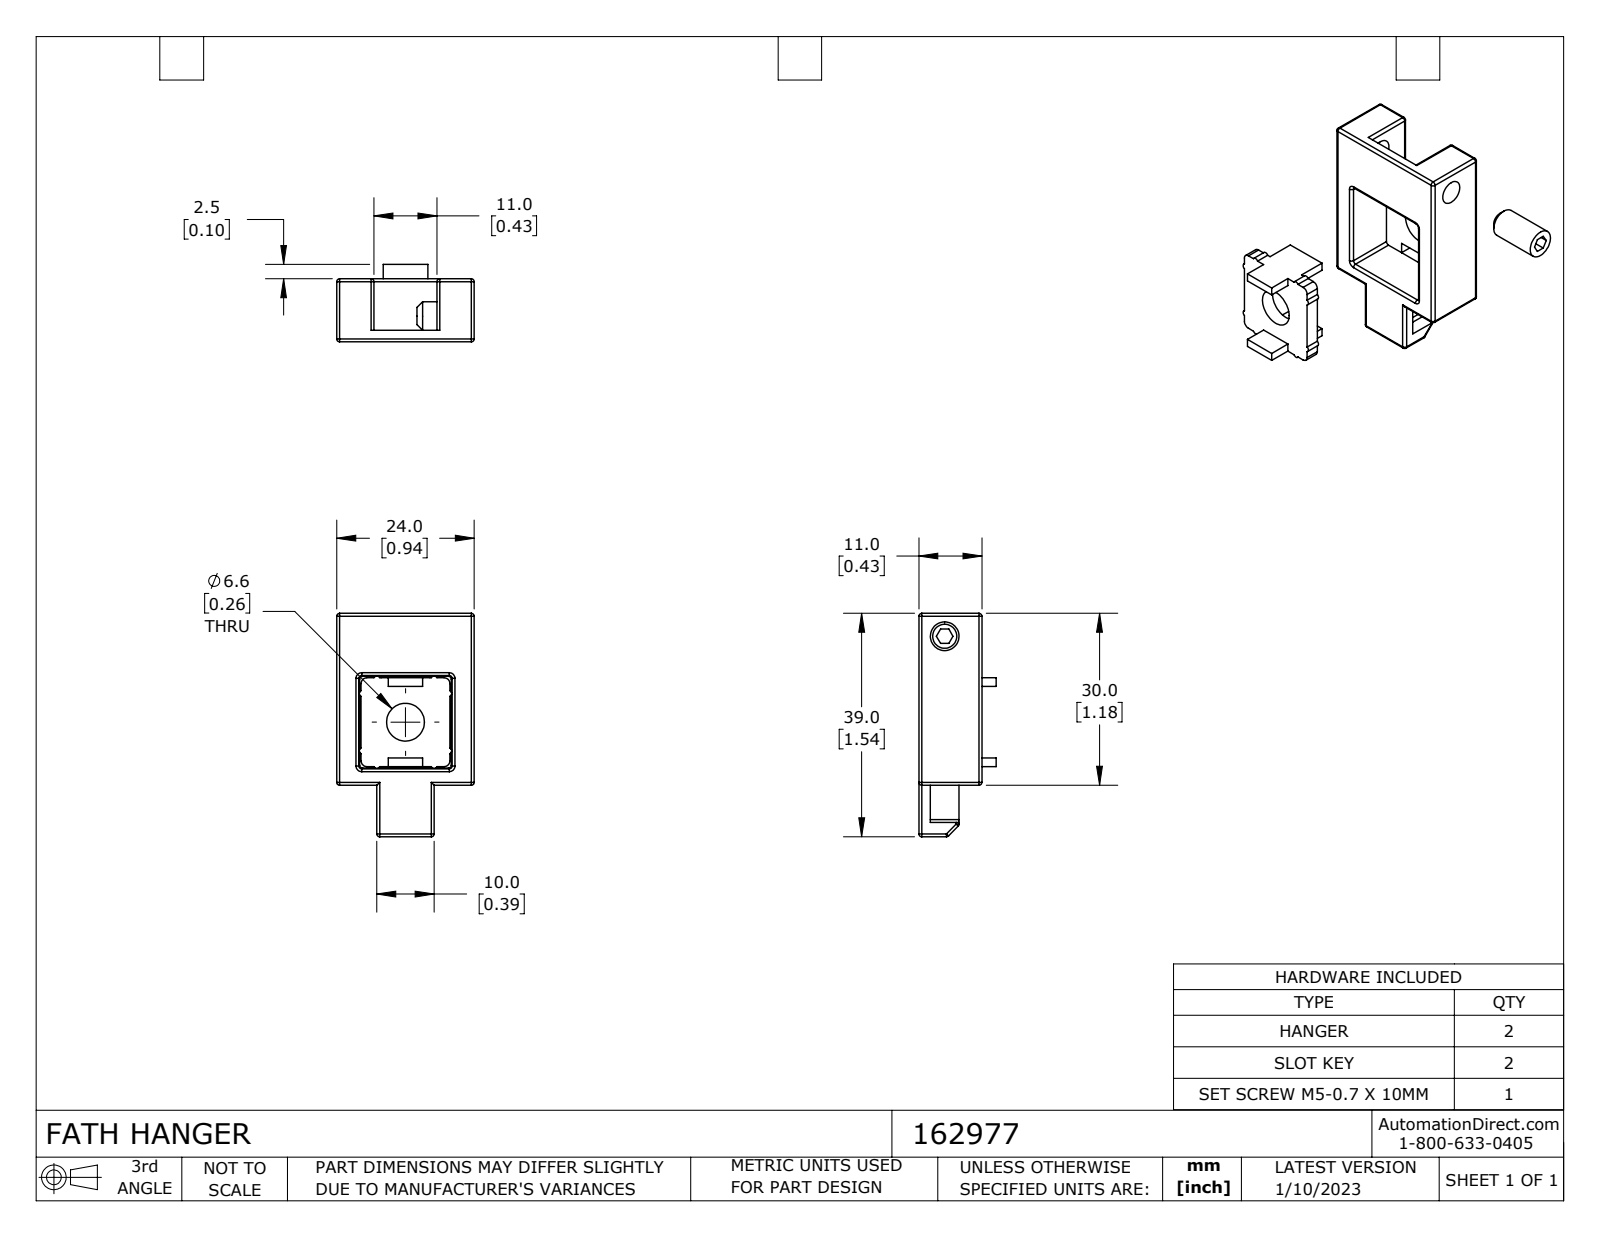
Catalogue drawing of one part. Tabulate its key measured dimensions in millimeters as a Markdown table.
| quantity | value |
| --- | --- |
| part name | 162977 |
| STEP written by | SolidWorks 2021 (CONFIG_CONTROL_DESIGN) |
| units | millimeters |
| bodies | 3 solids, 159 faces (73 planar, 64 cylindrical, 22 other) |
| overall size | 39 × 24 × 13.5 |
| volume | 5 690 mm³ |
| surface area | 4 861 mm² |
| round holes (diameter × count) | 4.2 × 1, 6.6 × 1 |
| round bosses / shafts (diameter × count) | 5 × 1 |
| partial cylindrical surfaces (radius × count) | 0.5 × 38, 0.6 × 8, 1 × 4 |
| main face-to-face distances | 2.5, 11, 8.5, 6.5, 5, 24, 14, 2, 9, 4 |
